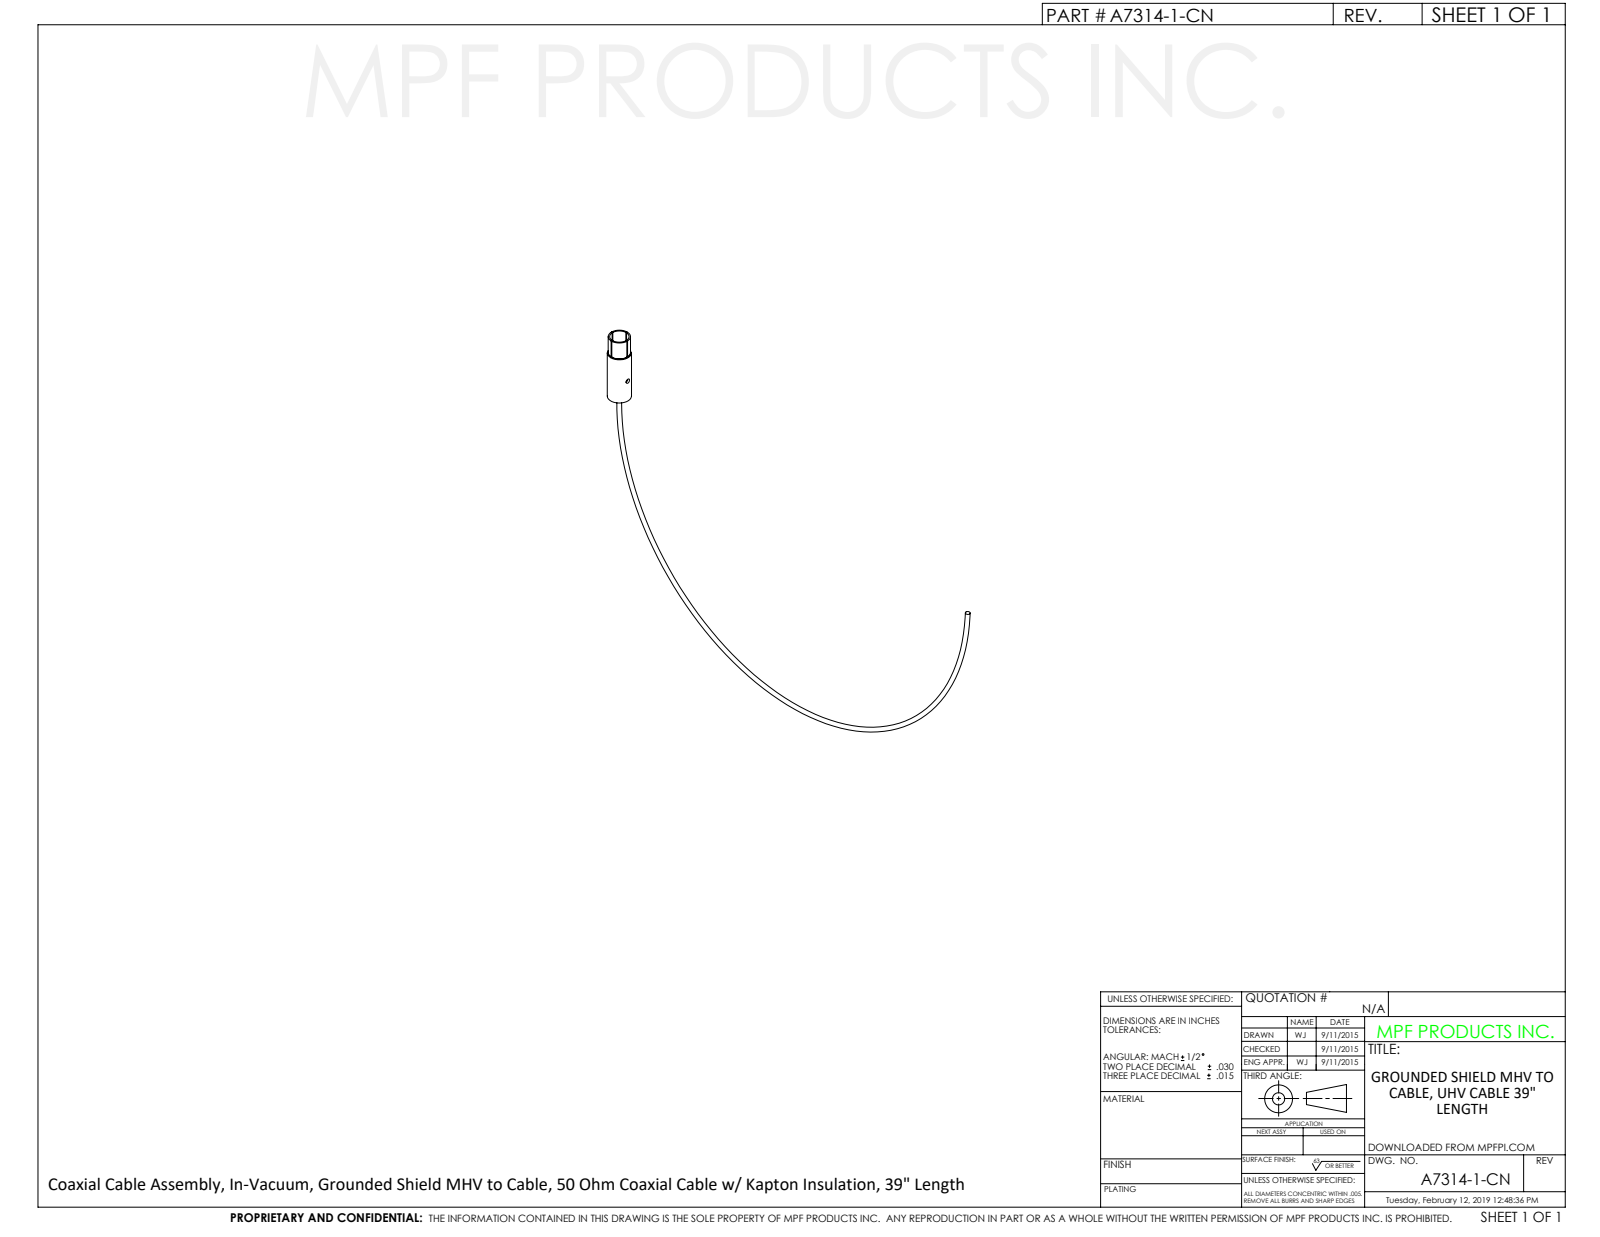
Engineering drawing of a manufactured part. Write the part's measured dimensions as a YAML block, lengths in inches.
part_name: "A7313-1-CN"
step_written_by: "SolidWorks 2012 (CONFIG_CONTROL_DESIGN)"
units: inches
bodies: {solids: 1, faces: 34, planar: 17, cylindrical: 12, other: 5}
overall_size: [10.587, 6.833, 0.75]
volume: 0.509
surface_area: 11.78
round_holes:
  - {diameter: 0.1, count: 2}
  - {diameter: 0.5, count: 1}
round_bosses_or_shafts:
  - {diameter: 0.75, count: 1}
  - {diameter: 0.71, count: 1}
face_to_face_distances: [1.5, 0.2, 1.3, 0.02, 1.1, 0.9, 0.4]
